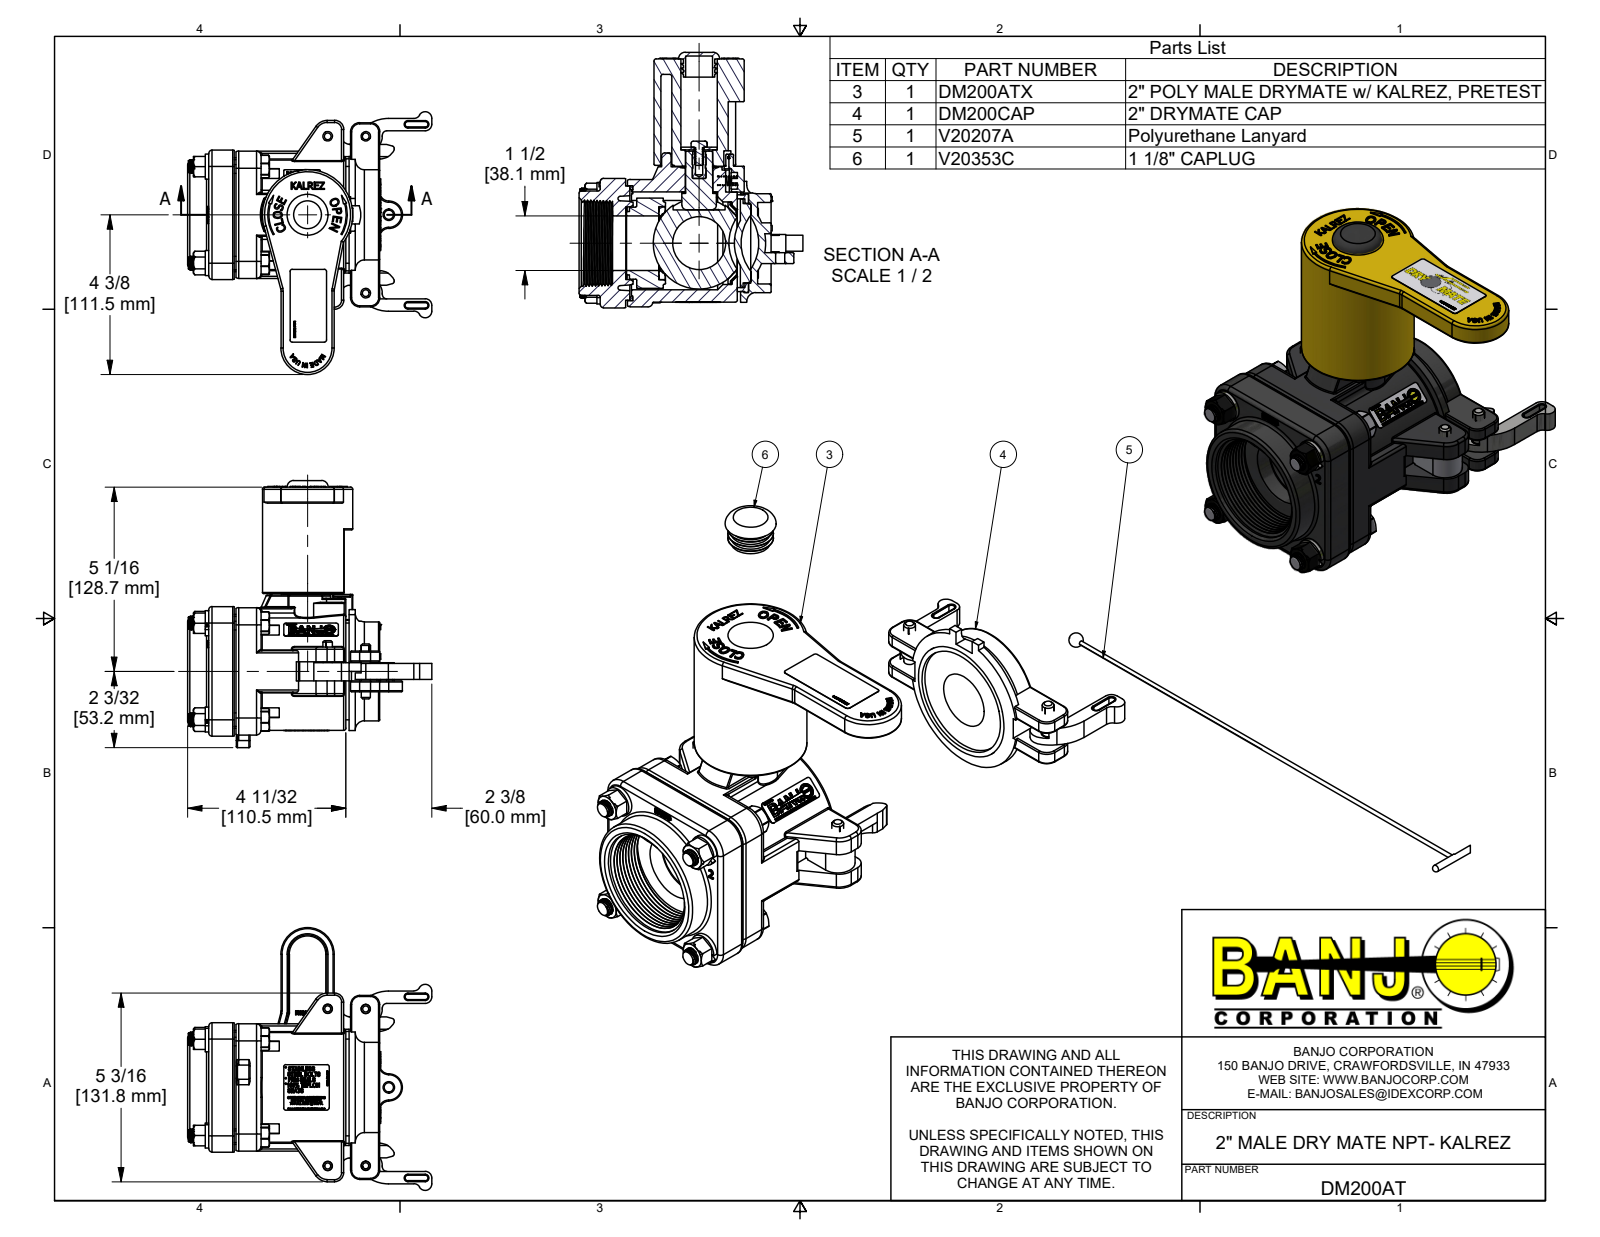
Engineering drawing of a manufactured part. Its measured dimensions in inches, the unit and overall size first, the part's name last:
Units: inches
Overall size (bounding box): 11.984 × 9.829 × 7.34
Round holes (diameter × count): ⌀0.25 ×5, ⌀0.375 ×5, ⌀0.256 ×4, ⌀0.307 ×4, ⌀0.385 ×4, ⌀0.406 ×4, ⌀0.42 ×4, ⌀0.125 ×3, ⌀0.196 ×1, ⌀0.2 ×1, ⌀0.227 ×1, ⌀0.281 ×1
Round bosses / shafts (diameter × count): ⌀0.324 ×60, ⌀0.687 ×4, ⌀0.375 ×4, ⌀0.26 ×4, ⌀0.249 ×4, ⌀0.28 ×3, ⌀2.48 ×2, ⌀3.25 ×1
Partial cylindrical surfaces — rounded edges, fillets, slot ends (radius × count): R0.03 ×104, R0.06 ×52, R0.02 ×20, R0.01 ×12, R0.125 ×10, R0.25 ×10, R0.09 ×8, R0.162 ×8
Main face-to-face distances: 3.07, 0.298, 3.04, 2.955, 0.75, 3.77, 0.297, 0.03, 3.53, 0.25
Hole centre spacings: 2.653, 1.872, 1.88, 2.648, 2.658, 3.752, 0.95, 1.646
Volume: 49.91 in³ · Surface area: 435.7 in²
Bodies: 47 solids, 6365 faces (3106 planar, 898 cylindrical, 2361 other)
Part name (STEP PRODUCT): DM200AT; DM200ATX; DM20254; DM20254MY (+8 more)
STEP written by: Autodesk Inventor 2022 (AUTOMOTIVE_DESIGN)
